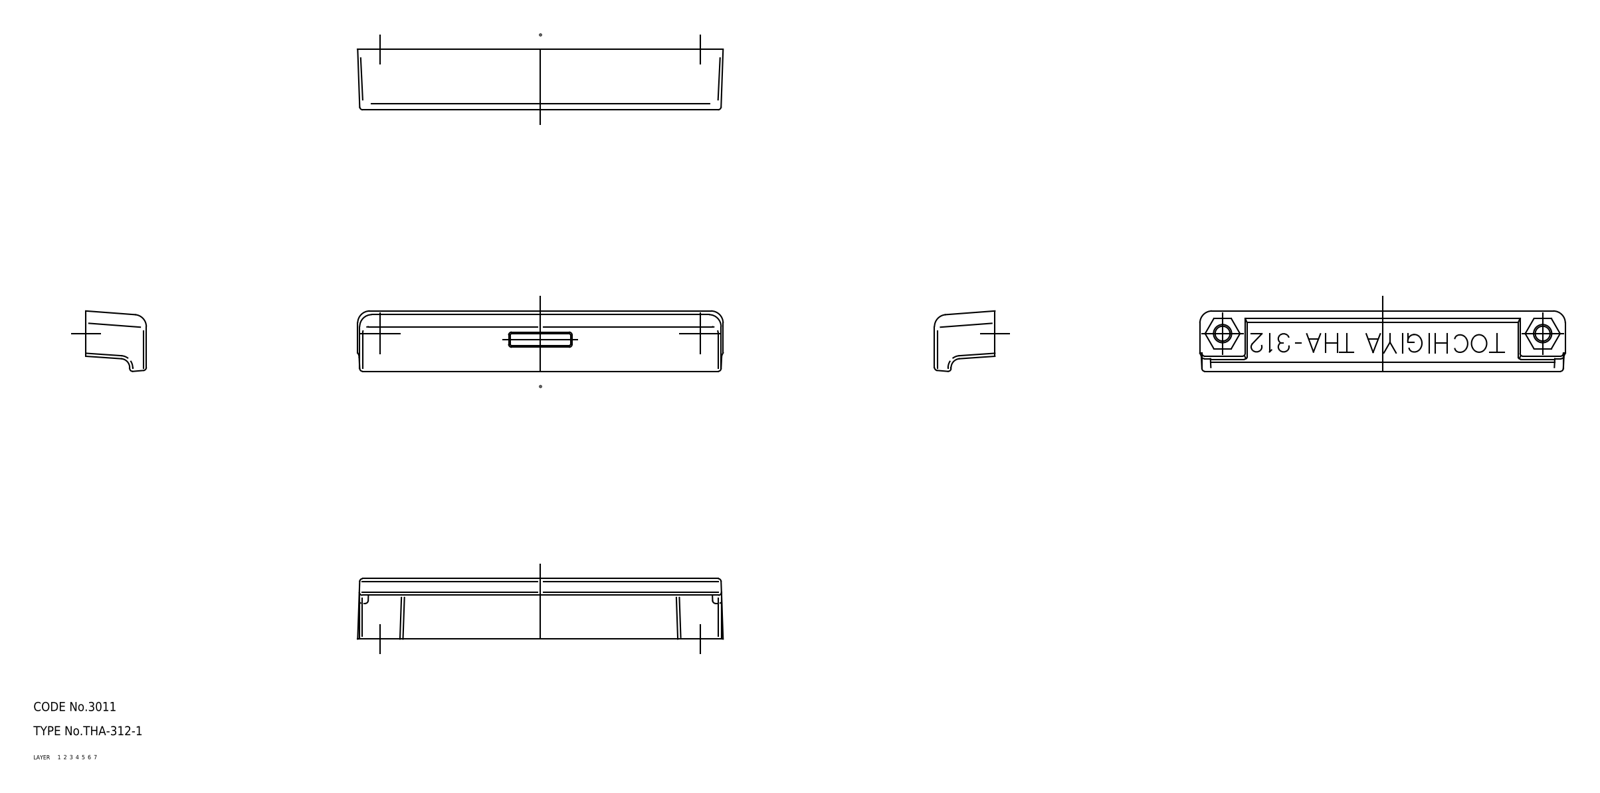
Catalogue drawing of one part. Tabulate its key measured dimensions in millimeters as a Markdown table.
| quantity | value |
| --- | --- |
| part name | insert; pull; THA_312_1_18299_36 |
| STEP written by | CADfix (AUTOMOTIVE_DESIGN) |
| units | millimeters |
| bodies | 3 solids, 94 faces (0 planar, 0 cylindrical, 94 other) |
| overall size | 121 × 20 × 20 |
| volume | 17 085 mm³ |
| surface area | 13 805 mm² |
